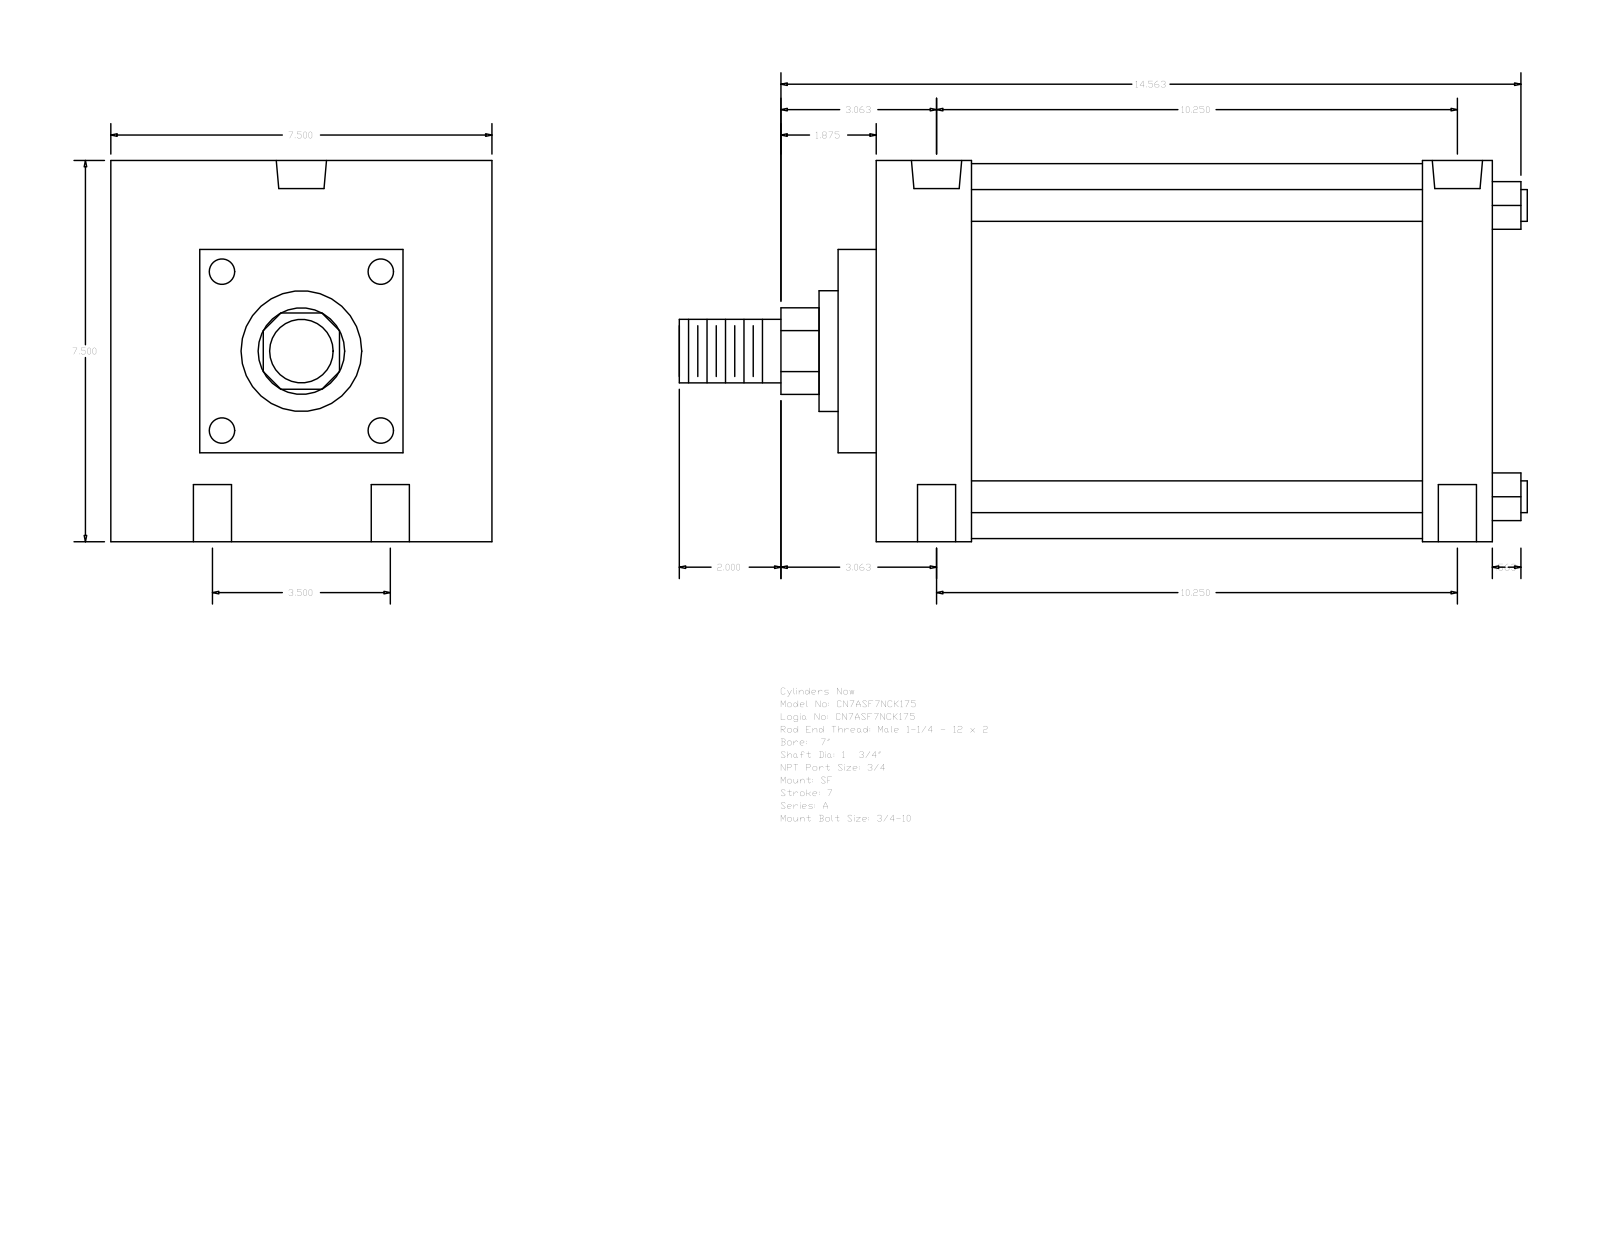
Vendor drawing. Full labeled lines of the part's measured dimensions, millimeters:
Part name (STEP PRODUCT): A_SF__0700_1.75
STEP written by: GSSL Pune (CONFIG_CONTROL_DESIGN)
Units: millimetres
Bodies: 0 solids, 93 faces (67 planar, 26 cylindrical, 0 other)
Overall size (bounding box): 423.86 × 190.5 × 190.5
Round holes (diameter × count): ⌀19.05 ×4, ⌀15.08 ×2, ⌀25.12 ×2
Round bosses / shafts (diameter × count): ⌀15.88 ×4, ⌀187.32 ×1, ⌀60.33 ×1, ⌀44.45 ×1, ⌀31.75 ×1
Partial cylindrical surfaces — rounded edges, fillets, slot ends (radius × count): R21.63 ×1
Main face-to-face distances: 190.5, 307.98, 146.05, 19.05, 47.63, 273.06, 225.43, 260.35, 34.92, 44.45
Hole centre spacings: 44.45, 264.12, 260.35, 88.9, 275.11, 249.23
